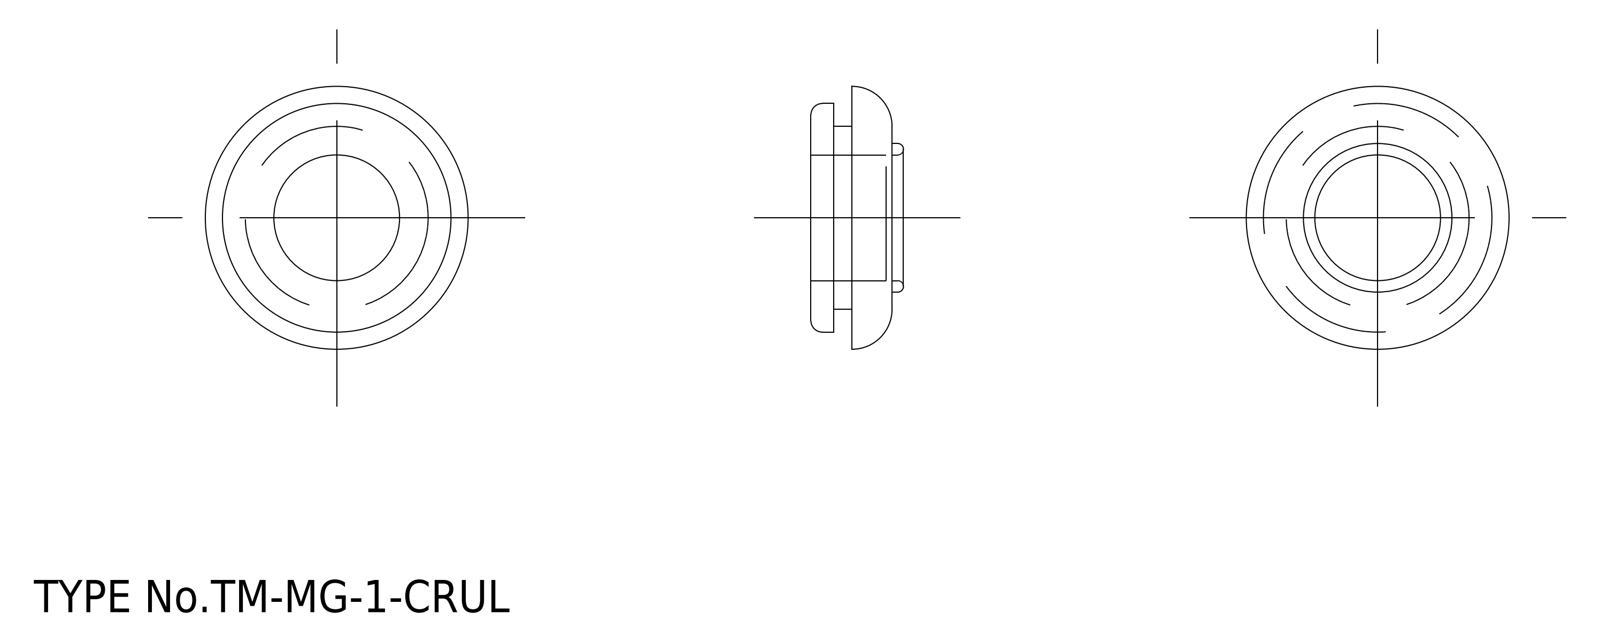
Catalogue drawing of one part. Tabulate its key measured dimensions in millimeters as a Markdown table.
| quantity | value |
| --- | --- |
| STEP written by | spGate 15.6.1 (AUTOMOTIVE_DESIGN) |
| units | millimeters |
| bodies | 1 solid, 22 faces (6 planar, 10 cylindrical, 6 other) |
| overall size | 23 × 23 × 8.1 |
| volume | 1 621 mm³ |
| surface area | 1 662 mm² |
| round holes (diameter × count) | 11 × 1 |
| round bosses / shafts (diameter × count) | 20 × 1, 16 × 1, 13 × 1 |
| main face-to-face distances | 3.5, 3.6, 7.1, 2, 1.6, 5.1, 6.6, 4.6, 3, 0.5 |
